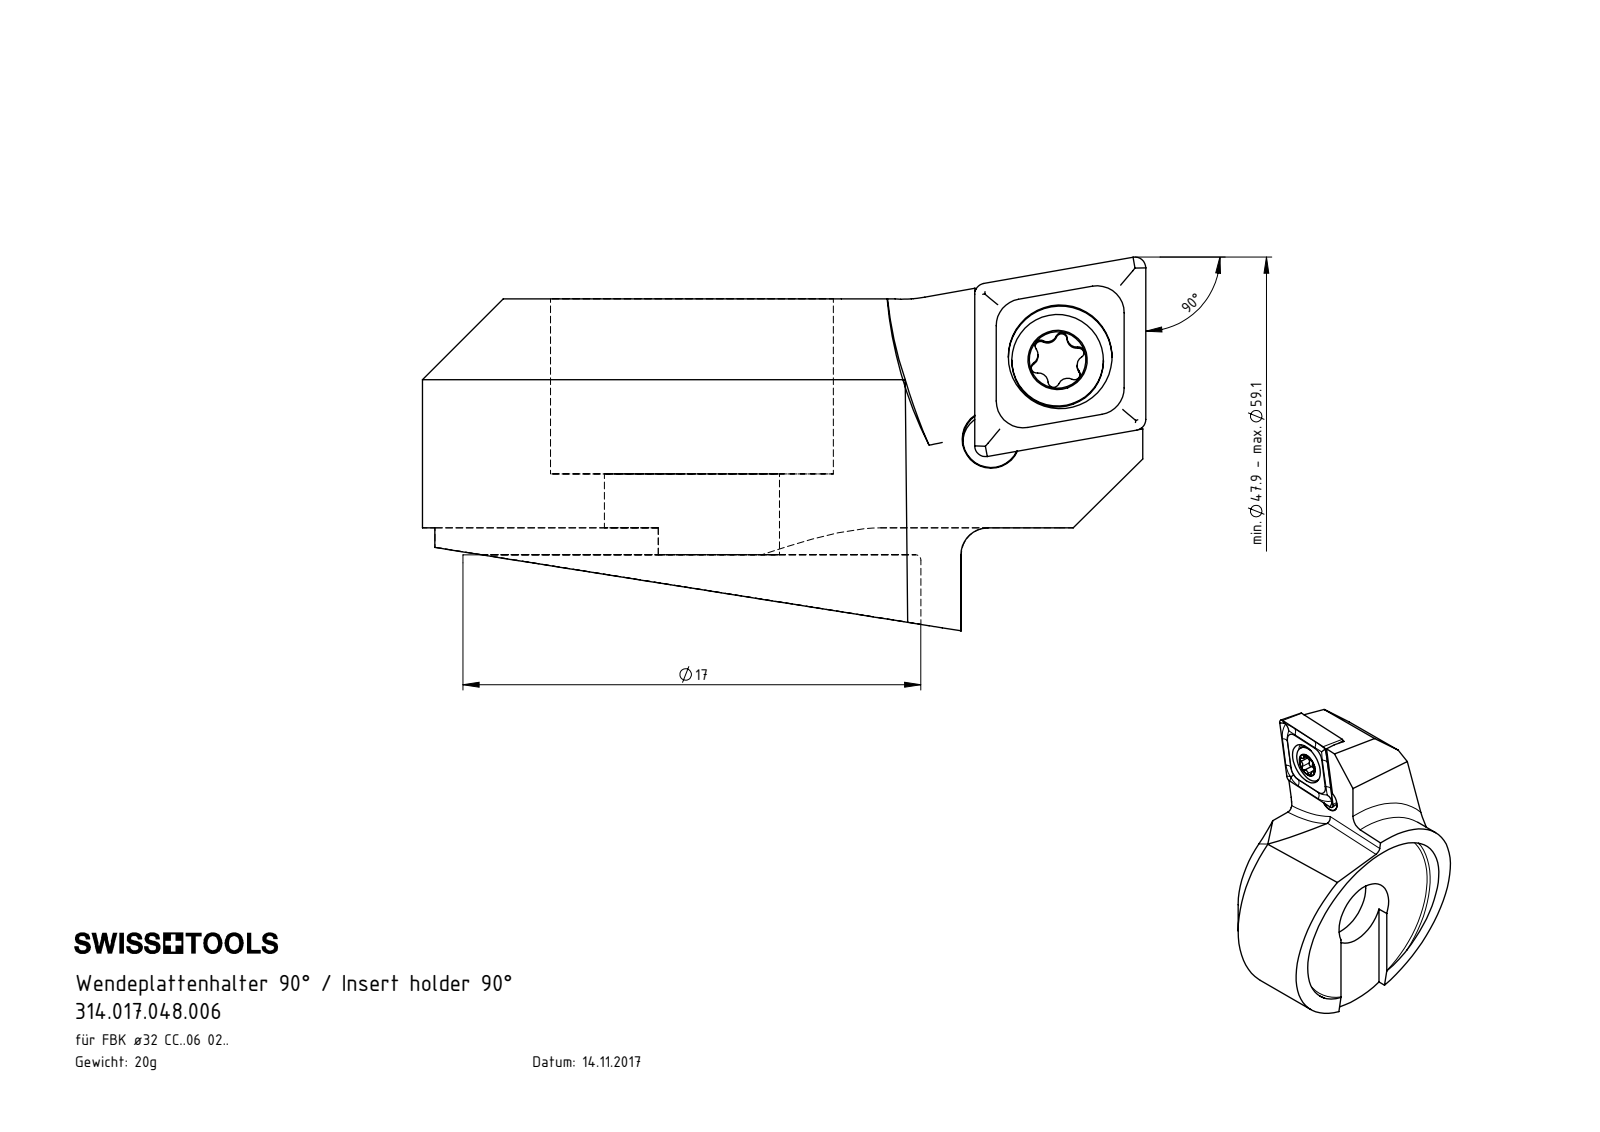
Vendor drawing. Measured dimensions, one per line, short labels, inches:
name: 314.017.048.006; F32-WCA.001.011_C_fertigbearbeitet; CCMT060204; WCA-ER2.001.006_A
written by: SolidWorks 2017 (CONFIG_CONTROL_DESIGN)
unit: in
bodies: 3 solids, 134 faces (38 planar, 42 cylindrical, 54 other)
size: 1.057 × 0.787 × 0.546
volume: 0.155 in³; area: 2.968 in²
holes: 1× ⌀0.081, 1× ⌀0.083, 1× ⌀0.11, 1× ⌀0.152, 1× ⌀0.256, 1× ⌀0.413
bosses: 1× ⌀0.787, 1× ⌀0.134, 1× ⌀0.098
rounds: 6× R0.008, 5× R0.014, 2× R0.02, 1× R0.014, 1× R0.197, 1× R0.335, 1× R0.591
face distances: 0.039, 0.335, 0.374, 0.256, 0.079, 0.118, 0.09, 0.089, 0.094, 0.094
hole spacings: 0.151, 0.157
